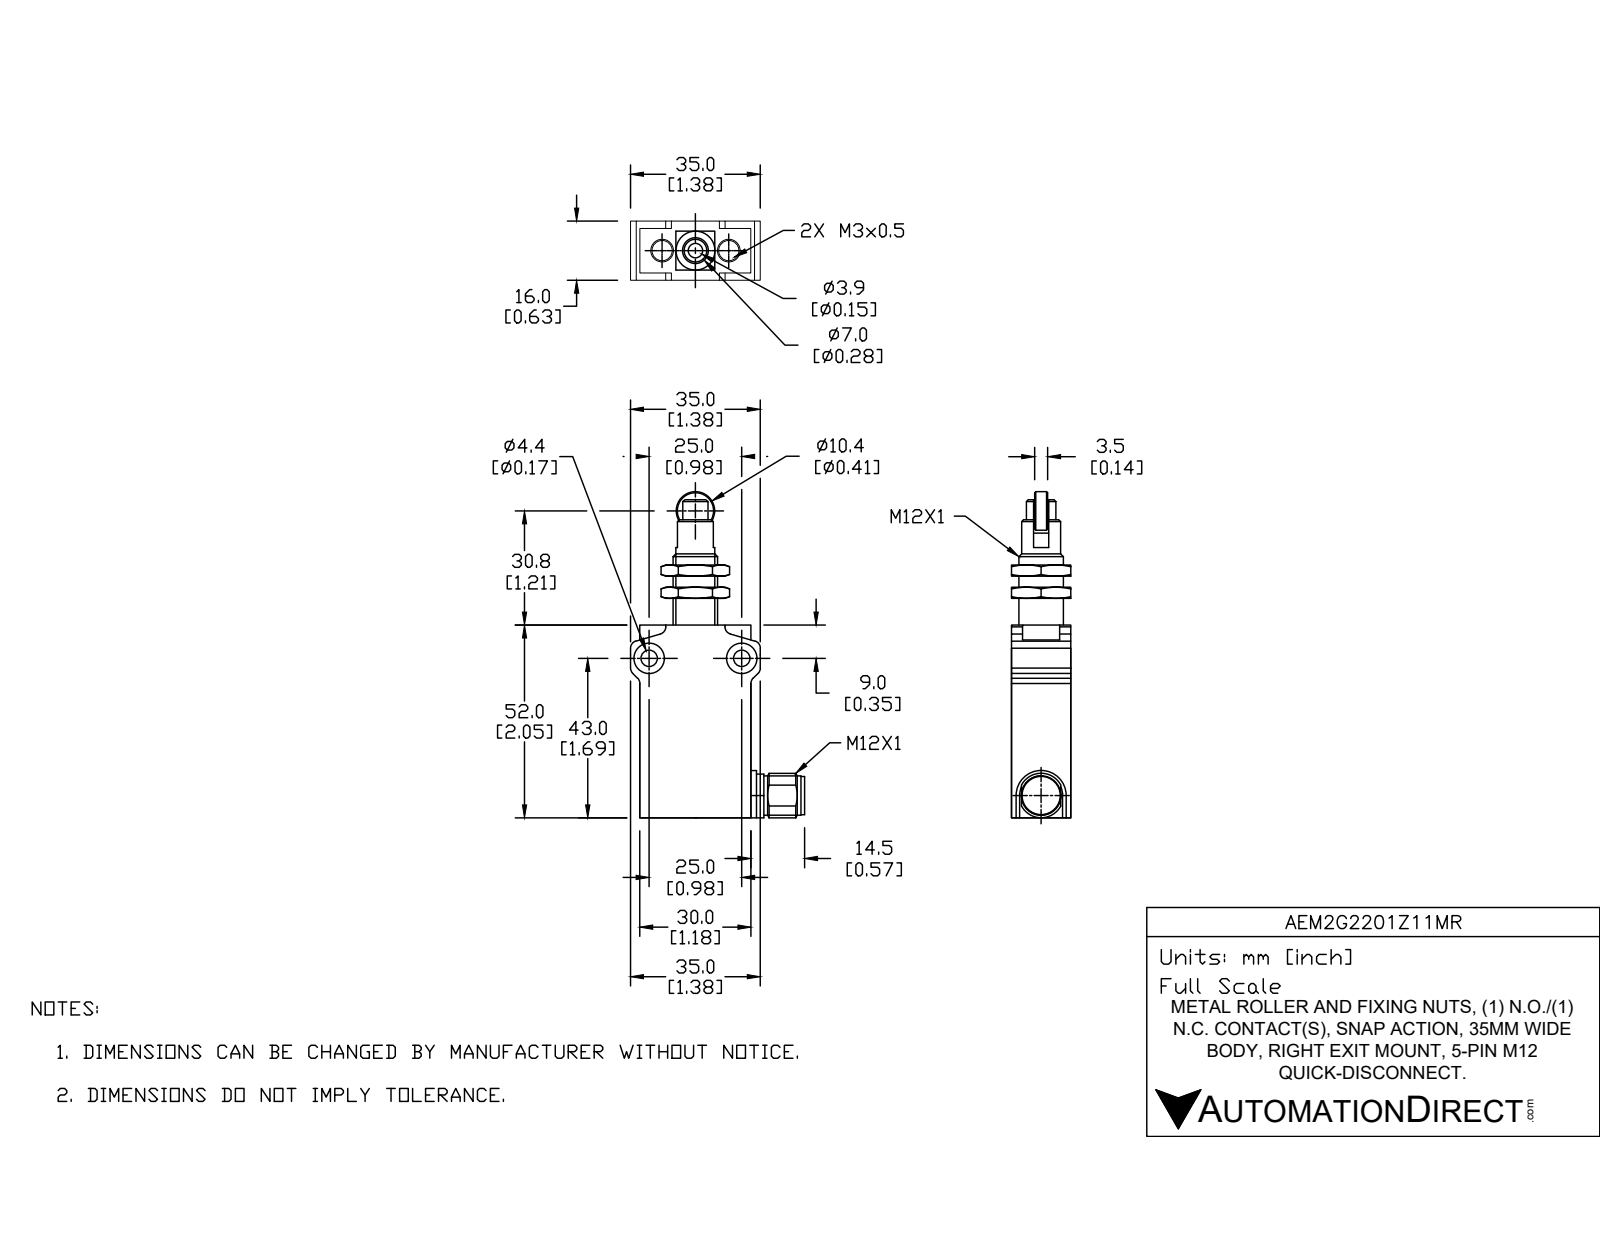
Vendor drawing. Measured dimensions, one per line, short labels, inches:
name: AEM2G2201Z11MR
written by: SolidWorks 2019 (AUTOMOTIVE_DESIGN)
unit: in
bodies: 7 solids, 199 faces (83 planar, 53 cylindrical, 63 other)
size: 3.465 × 1.831 × 0.63
volume: 1.786 in³; area: 18.39 in²
holes: 2× ⌀0.118, 2× ⌀0.173, 2× ⌀0.323, 1× ⌀0.317, 1× ⌀0.472
bosses: 1× ⌀0.472, 1× ⌀0.417, 1× ⌀0.413, 1× ⌀0.409, 1× ⌀0.406, 1× ⌀0.313, 1× ⌀0.22
rounds: 8× R0.079, 1× R0.256
face distances: 0.63, 1.181, 0.472, 0.118, 0.236, 2.047, 1.858, 0.189, 0.354, 0.157
hole spacings: 0.374, 0.748, 0.984
